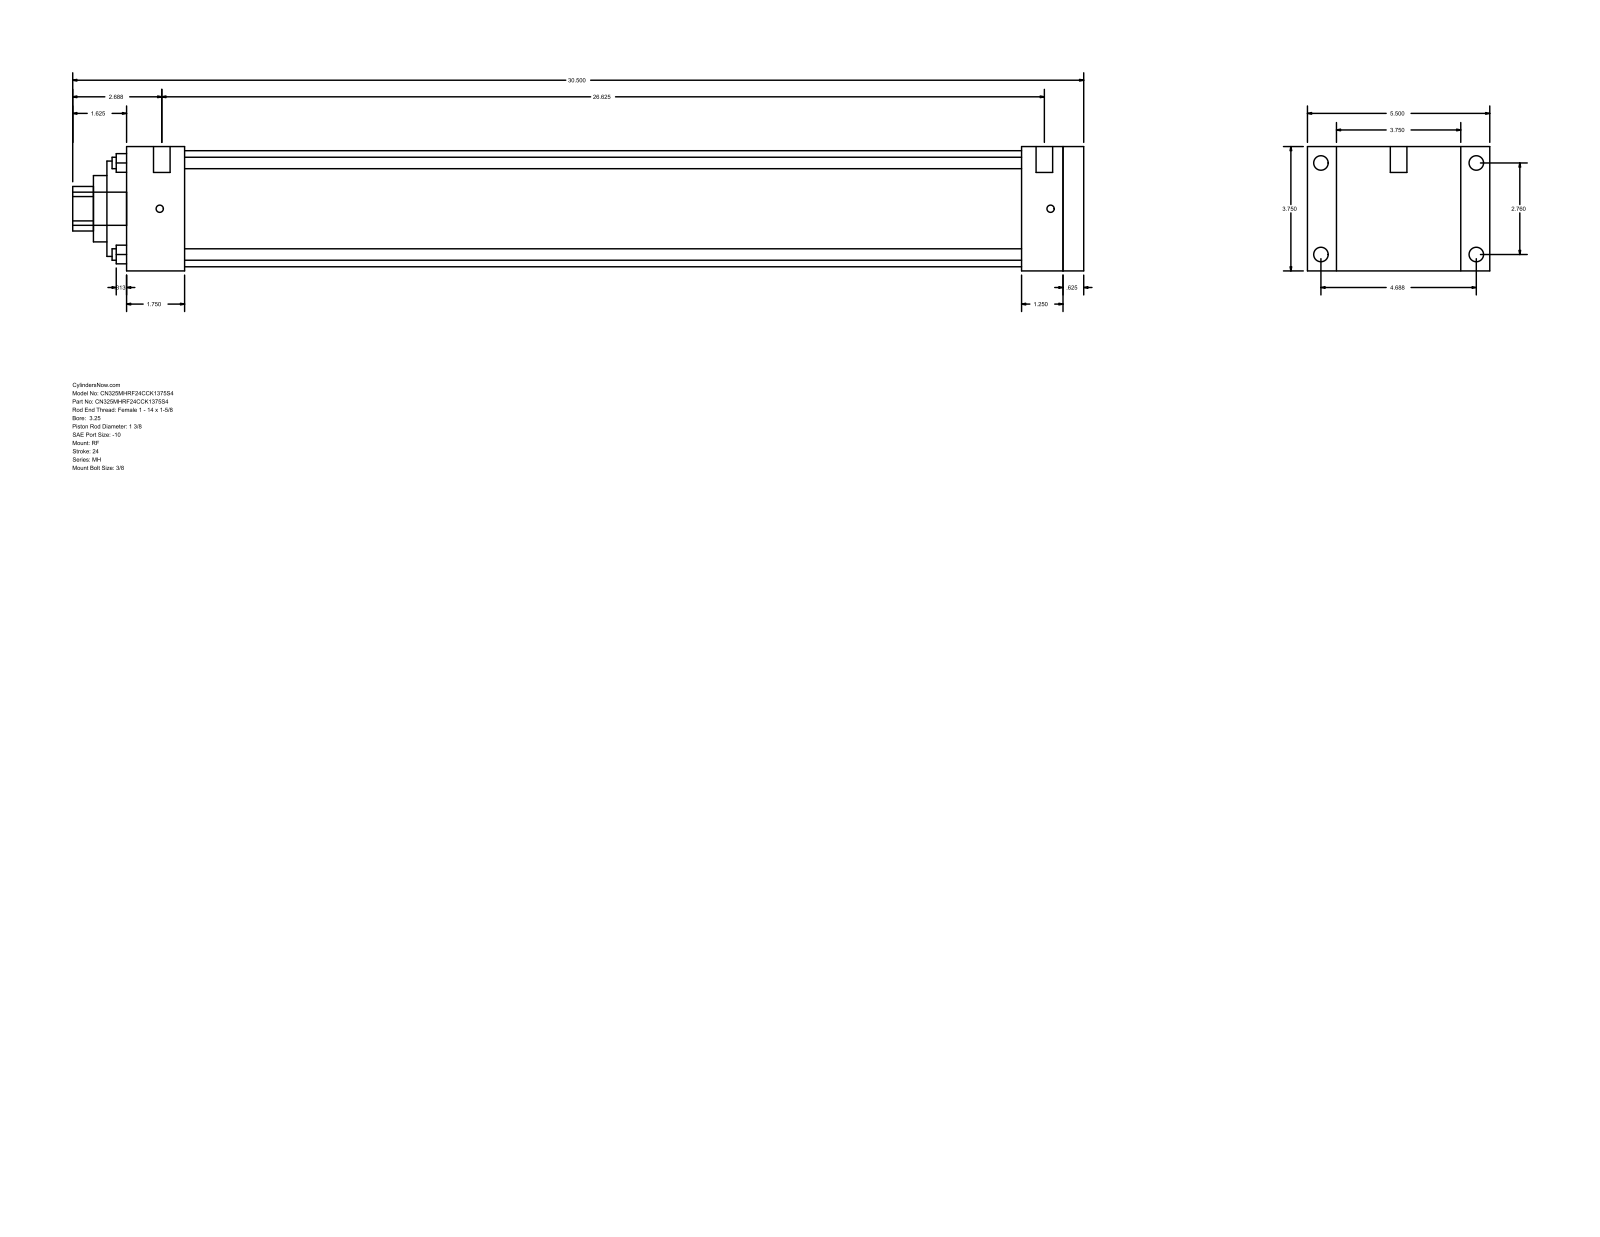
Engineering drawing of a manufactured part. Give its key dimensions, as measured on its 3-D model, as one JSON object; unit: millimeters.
{"part_name": "MH_RF__0325_1.375", "step_written_by": "GSSL Pune (CONFIG_CONTROL_DESIGN)", "units": "millimeters", "bodies": {"solids": 0, "faces": 94, "planar": 65, "cylindrical": 29, "other": 0}, "overall_size": [774.7, 139.7, 95.25], "round_holes": [[8.76, 4], [34.92, 1], [50.8, 1], [73.03, 1], [88.9, 1]], "round_bosses_or_shafts": [[11.13, 4], [5.56, 4], [12.7, 2], [25.4, 1]], "partial_cylinders_radius": [[17.06, 1]], "face_to_face_distances": [95.24, 733.43, 717.56, 15.87, 22.23, 117.47, 44.45, 673.11, 688.98, 685.81], "hole_center_spacings": [49.57, 70.1, 99.14]}
